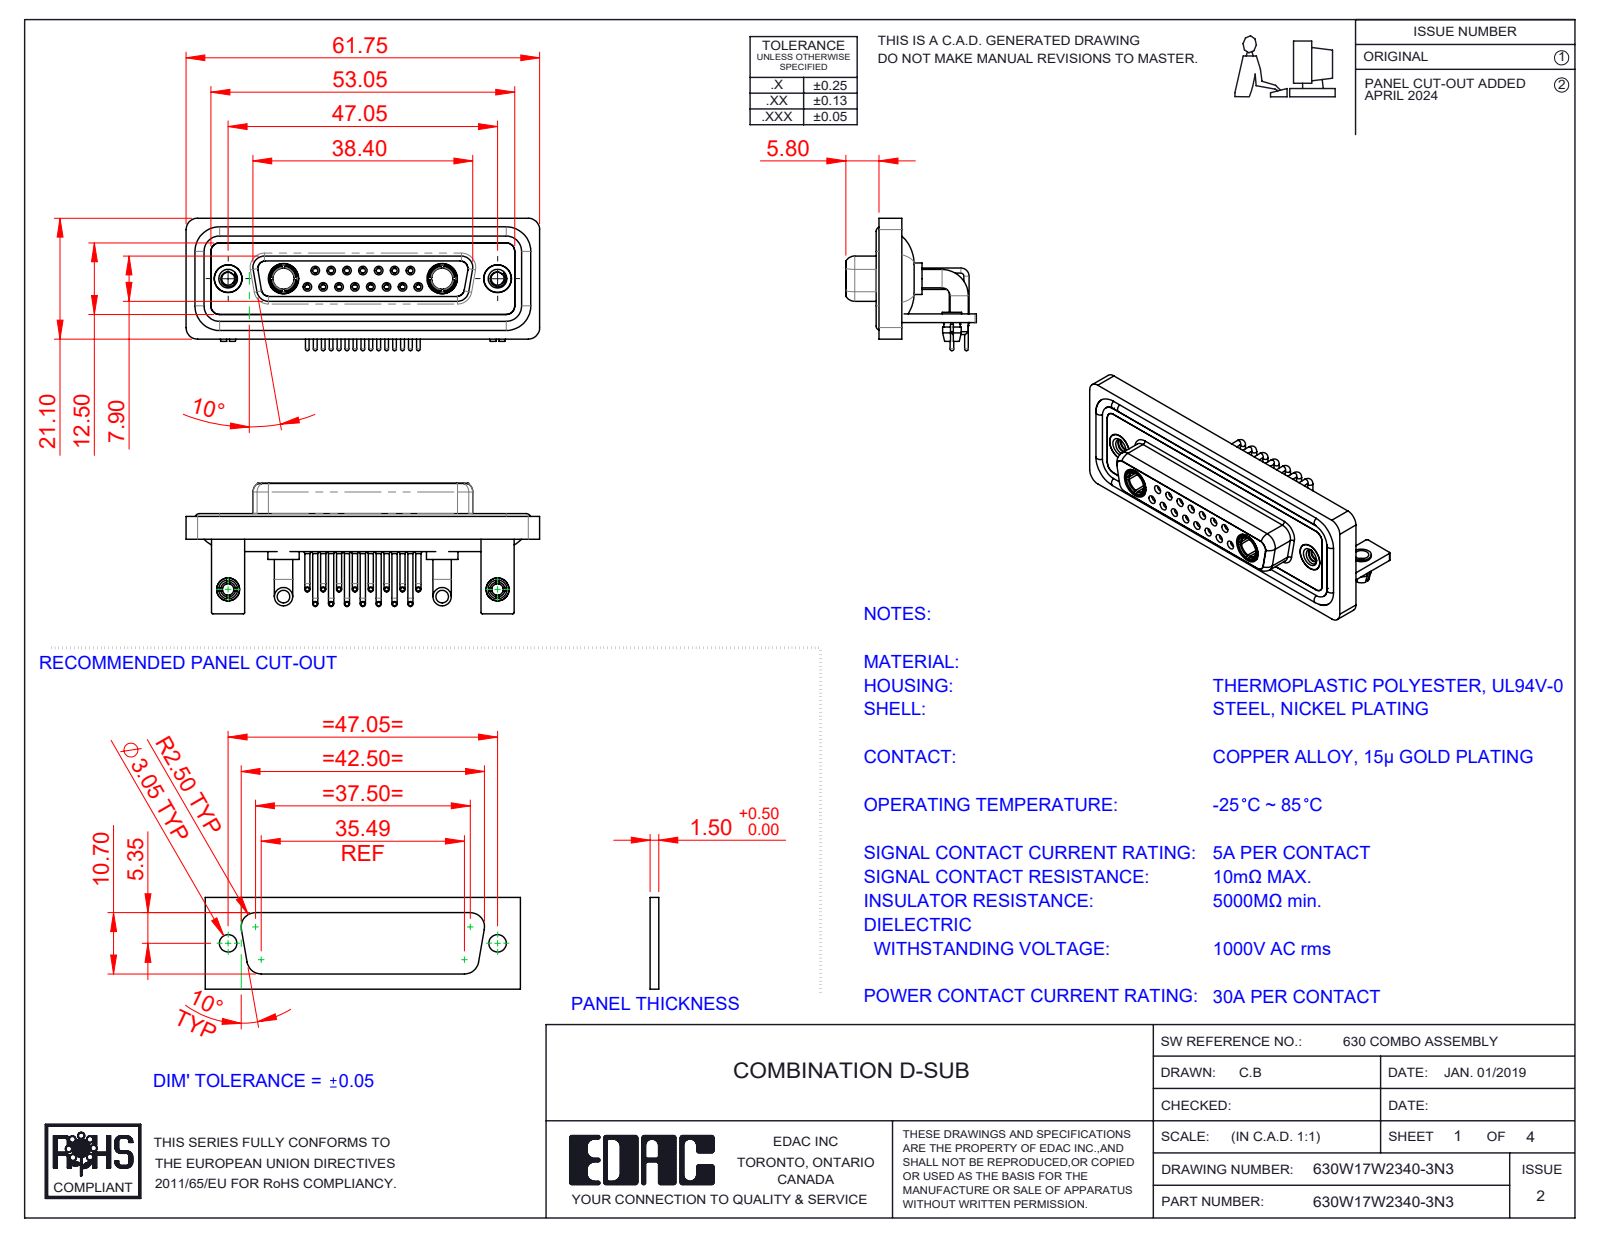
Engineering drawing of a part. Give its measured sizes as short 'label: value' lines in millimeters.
name: 630Combo Housing_17W2; 630Combo Stabilizer Bracket_50 Contacts; 630Combo Contact Row 2_50 Contacts; 630Combo Shell Front_25 Contacts (+7 more)
written by: SolidWorks 2023 (CONFIG_CONTROL_DESIGN)
unit: mm
bodies: 30 solids, 1477 faces (456 planar, 639 cylindrical, 382 other)
size: 61.75 × 23.12 × 22.8
volume: 8 945 mm³; area: 15 513 mm²
holes: 17× ⌀2, 15× ⌀0.9, 15× ⌀1.1, 15× ⌀1.5, 8× ⌀1.6, 7× ⌀1.7, 4× ⌀4.85, 2× ⌀2.26, 2× ⌀2.5, 2× ⌀3.2, 2× ⌀3.7, 2× ⌀4
bosses: 15× ⌀0.9, 15× ⌀0.65, 11× ⌀1.6, 4× ⌀3.2, 2× ⌀5.5, 2× ⌀5.2, 2× ⌀4.96, 2× ⌀4.95
rounds: 19× R2, 18× R1.5, 16× R0.25, 8× R1.35, 8× R1.6, 5× R0.5, 4× R0.6, 4× R0.65
face distances: 0.4, 1.8, 2.9, 3.7, 1.5, 4.1, 1.1, 1.4, 1.6, 3.1
hole spacings: 3.16, 2.77, 5.54, 8.31, 5.04, 7.49, 11.08, 5.03
